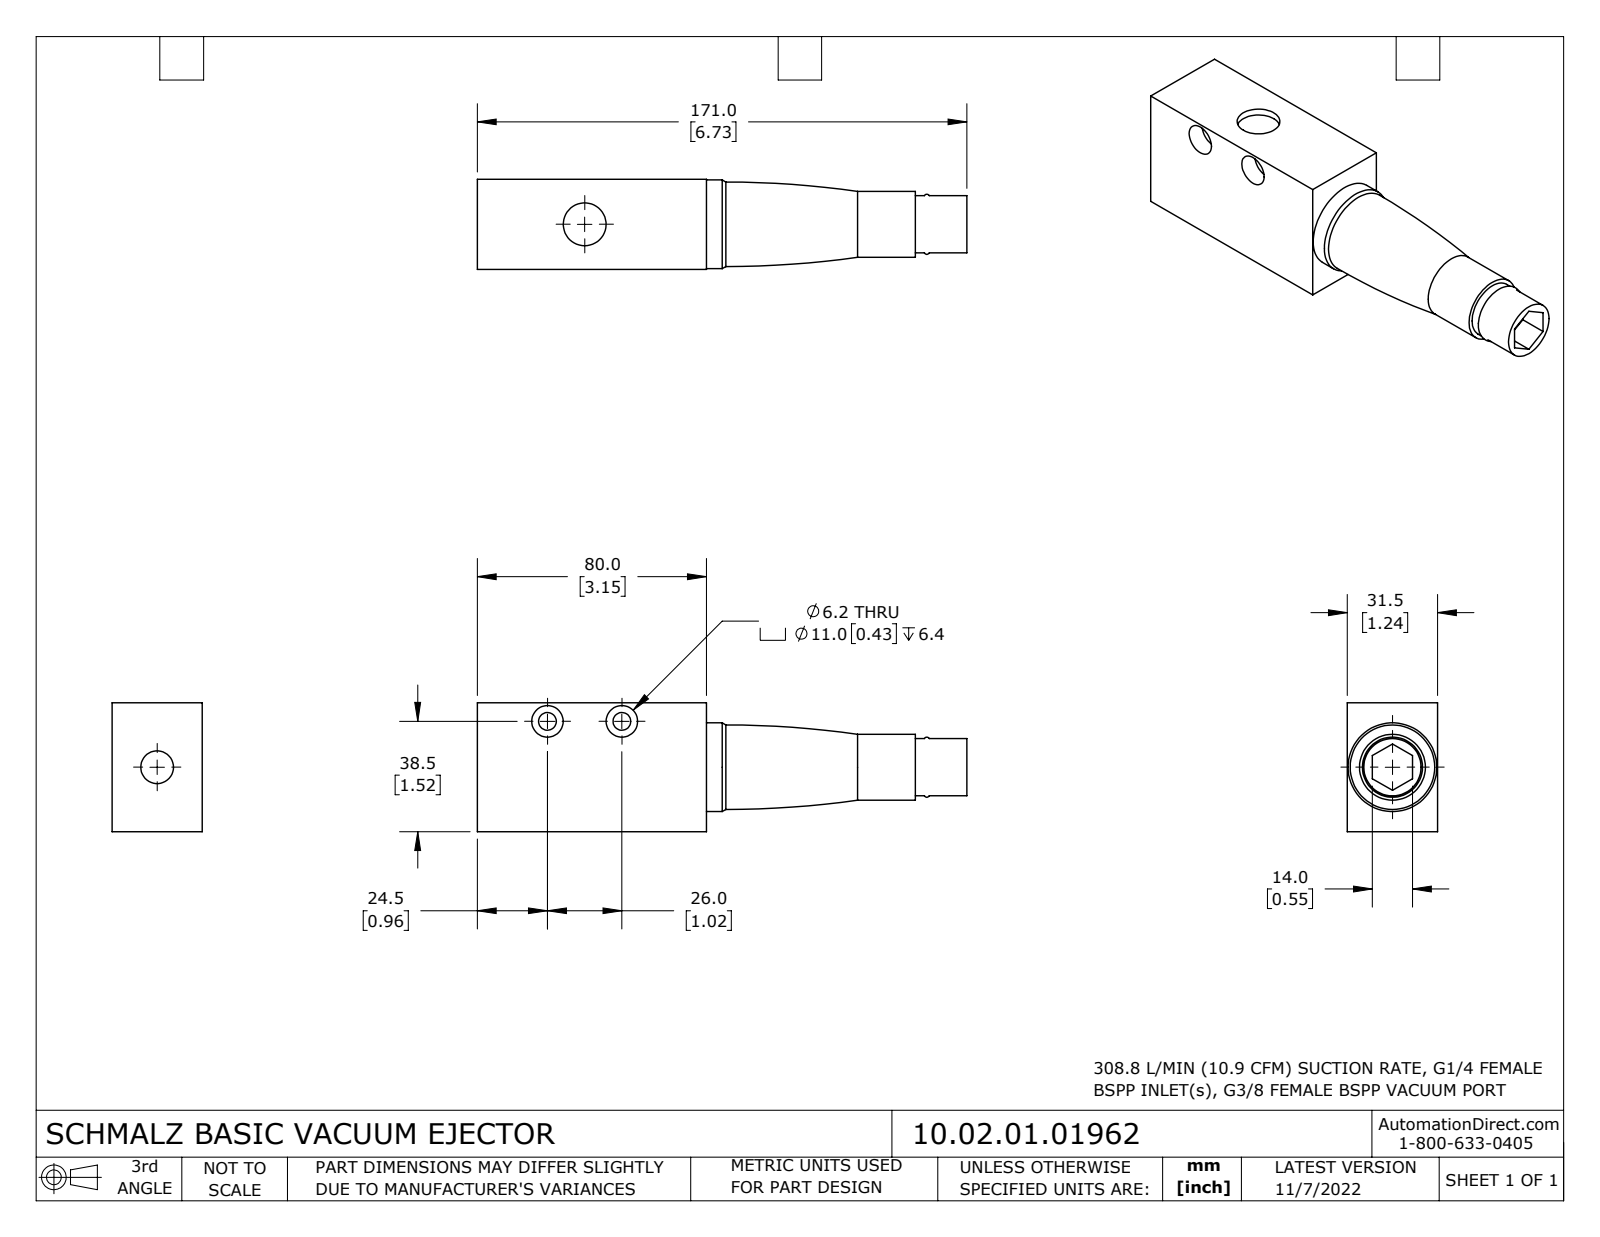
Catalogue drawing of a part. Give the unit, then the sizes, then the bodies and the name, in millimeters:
Units: millimetres
Overall size (bounding box): 171 × 45 × 31.5
Round holes (diameter × count): ⌀5 ×4, ⌀6.2 ×2, ⌀11 ×2, ⌀11.45 ×1, ⌀14.95 ×1, ⌀23 ×1, ⌀24 ×1, ⌀28 ×1
Round bosses / shafts (diameter × count): ⌀31 ×1, ⌀27 ×1, ⌀25 ×1, ⌀20 ×1
Main face-to-face distances: 31.5, 45, 80, 2.5, 75, 5, 77.5, 6.4, 25.1, 42.5
Hole centre spacings: 15.56, 22, 31.11, 26
Volume: 153 316 mm³ · Surface area: 29 514 mm²
Bodies: 4 solids, 86 faces (30 planar, 40 cylindrical, 16 other)
Part name (STEP PRODUCT): 10.02.01.01962
STEP written by: SolidWorks 2021 (CONFIG_CONTROL_DESIGN)
